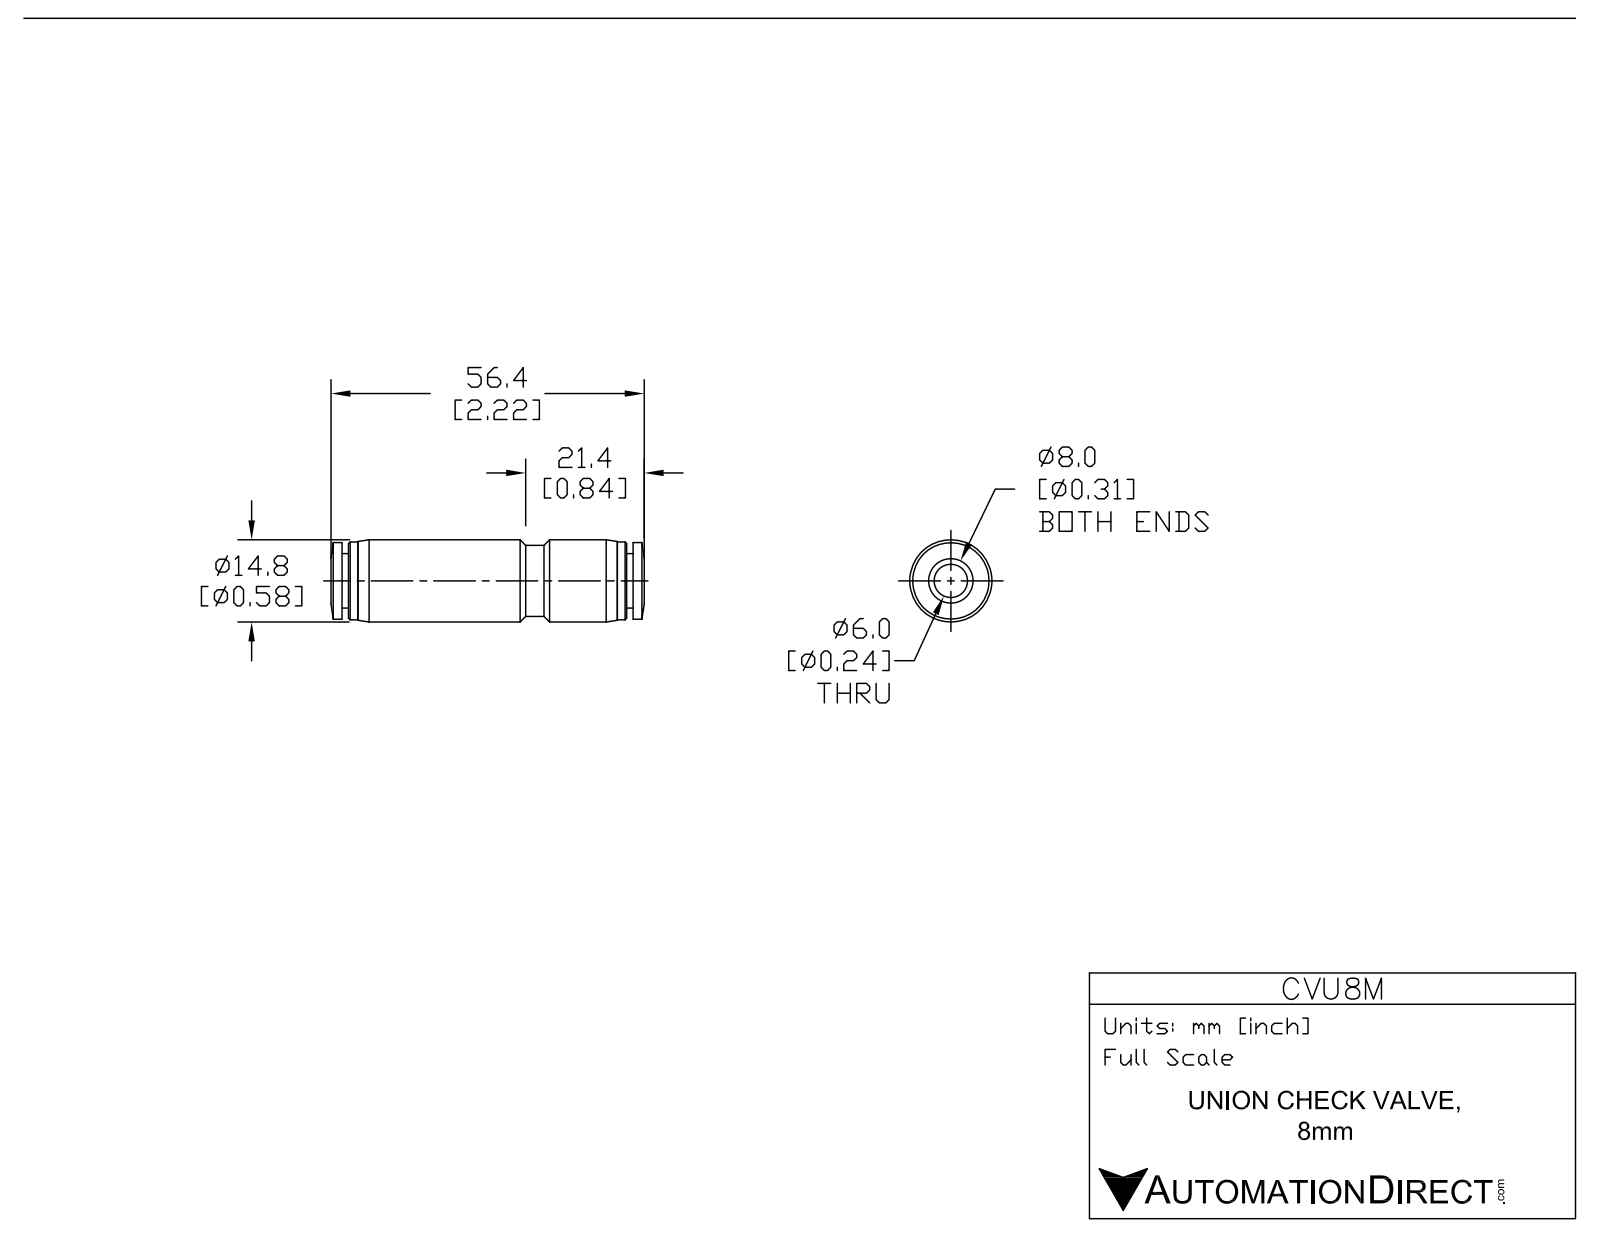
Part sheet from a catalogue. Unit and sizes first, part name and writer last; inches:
Units: inches
Overall size (bounding box): 2.22 × 0.583 × 0.583
Round holes (diameter × count): ⌀0.278 ×1, ⌀0.327 ×1
Round bosses / shafts (diameter × count): ⌀0.583 ×1, ⌀0.551 ×1, ⌀0.543 ×1, ⌀0.504 ×1, ⌀0.386 ×1, ⌀0.11 ×1
Partial cylindrical surfaces — rounded edges, fillets, slot ends (radius × count): R0.069 ×1, R0.287 ×1
Main face-to-face distances: 0.045, 2.018, 2.063, 1.972, 0.657, 1.406, 0.612, 1.36, 0.748, 0.124
Volume: 0.385 in³ · Surface area: 6.901 in²
Bodies: 1 solid, 76 faces (24 planar, 32 cylindrical, 20 other)
Part name (STEP PRODUCT): CVU8M
STEP written by: SolidWorks 2015 (AUTOMOTIVE_DESIGN)
